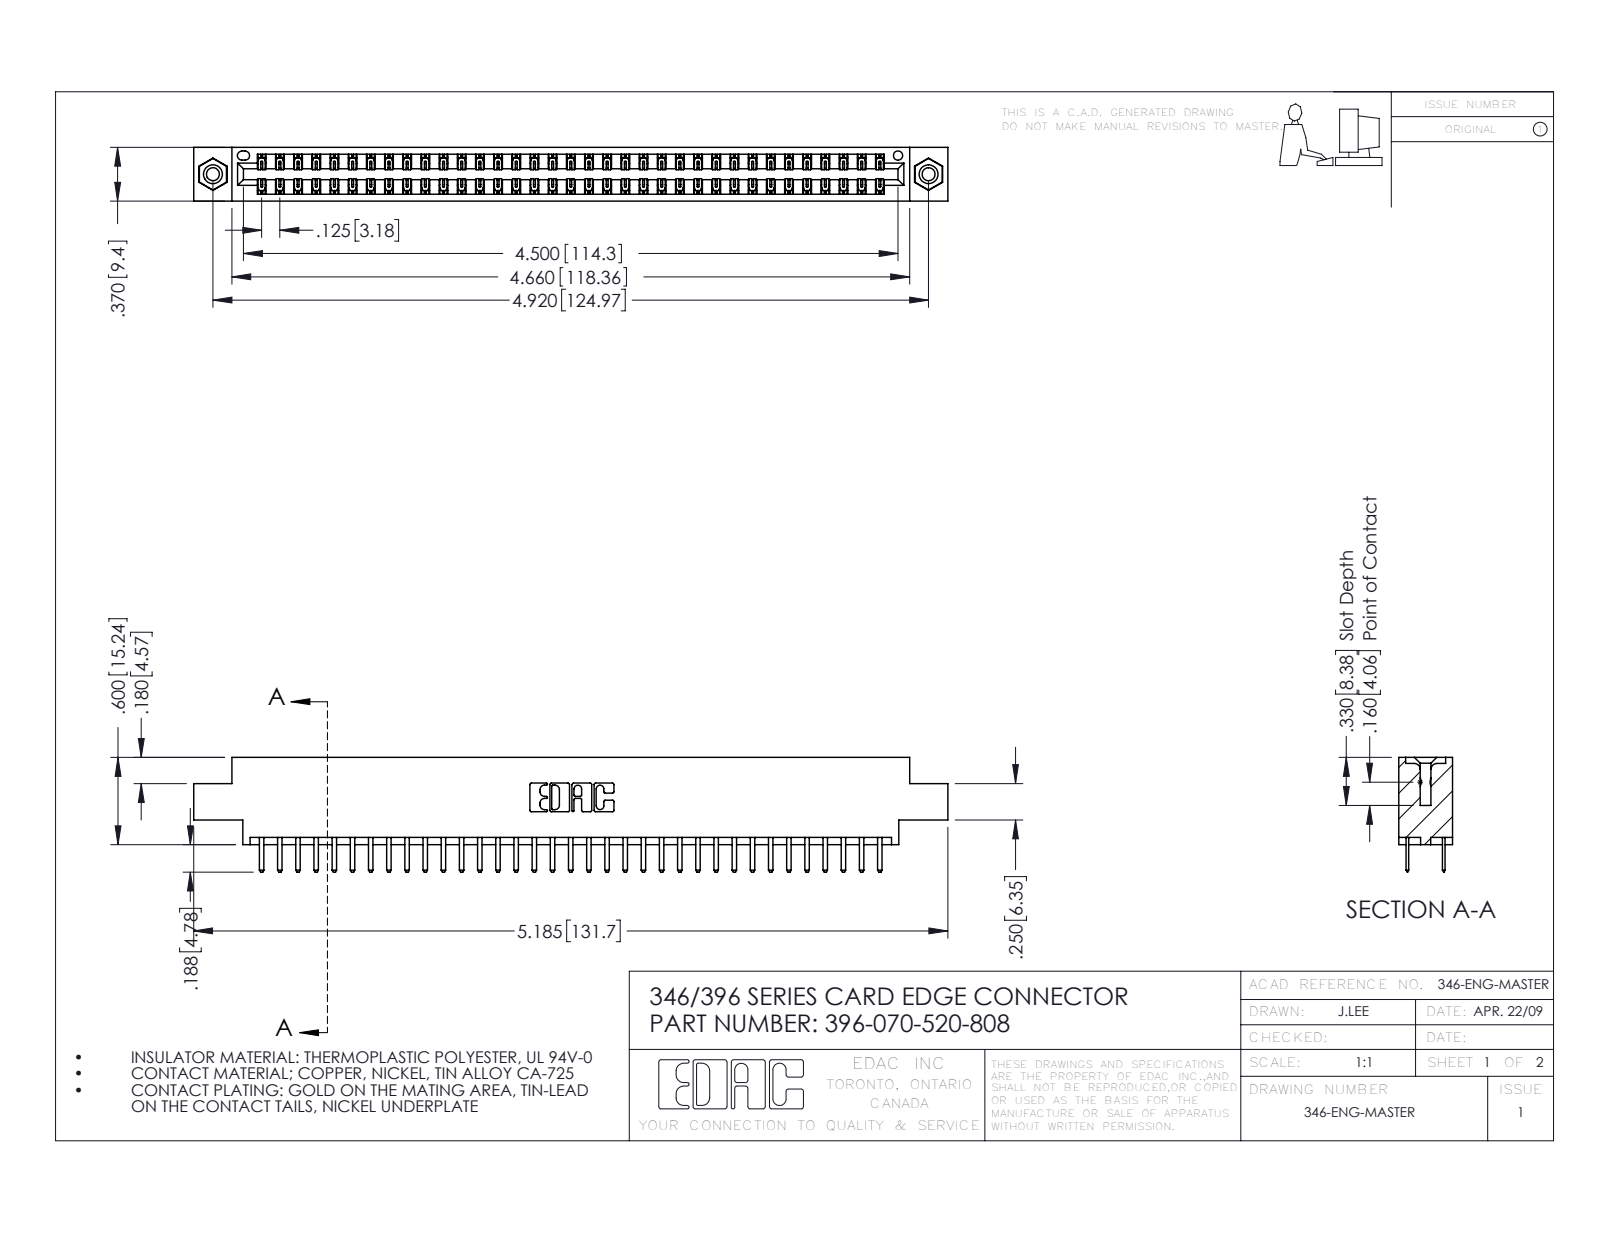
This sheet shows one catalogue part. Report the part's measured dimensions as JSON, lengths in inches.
{"part_name": "345-250-001_345-250-003-102; 396-070-520-808; 345-292-001_345-293-120; 346 Part_0.170 Offset - 0.156 Dia-TI", "step_written_by": "SolidWorks 2016 (CONFIG_CONTROL_DESIGN)", "units": "inches", "bodies": {"solids": 73, "faces": 4106, "planar": 2702, "cylindrical": 1388, "other": 16}, "overall_size": [5.185, 0.788, 0.37], "volume_in3": 0.769, "surface_area_in2": 26.86, "round_holes": [[0.089, 2], [0.125, 2], [0.156, 2], [0.064, 1]], "round_bosses_or_shafts": [[0.155, 2]], "partial_cylinders_radius": [[0.006, 105], [0.01, 74], [0.01, 22], [0.007, 6], [0.031, 6], [0.026, 3], [0.014, 2], [0.022, 2]], "face_to_face_distances": [0.048, 0.322, 0.37, 0.25, 0.275, 0.072, 0.298, 0.025, 0.222, 0.148], "hole_center_spacings": [0.246, 4.711, 4.92]}
